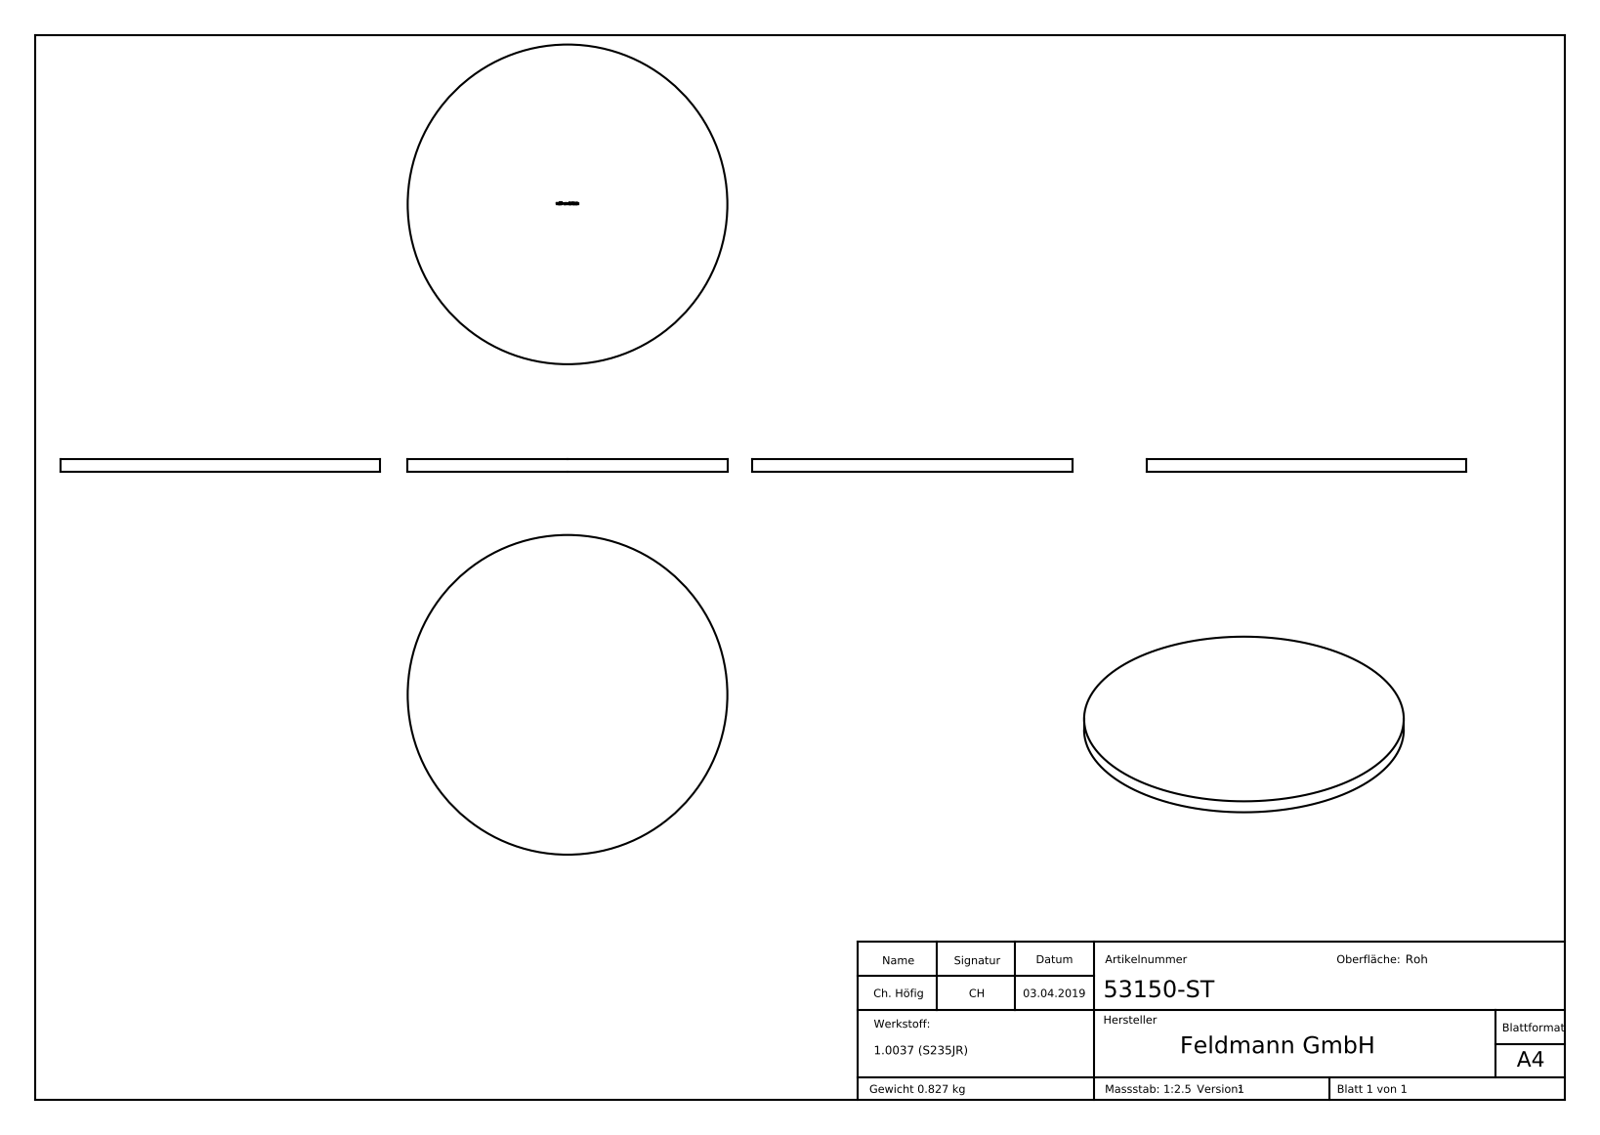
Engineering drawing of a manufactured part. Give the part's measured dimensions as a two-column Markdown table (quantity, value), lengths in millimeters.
| quantity | value |
| --- | --- |
| part name | 53150-ST |
| STEP written by | SolidWorks 2015 (CONFIG_CONTROL_DESIGN) |
| units | millimeters |
| bodies | 1 solid, 215 faces (111 planar, 2 cylindrical, 102 other) |
| overall size | 150 × 150 × 6 |
| volume | 106 029 mm³ |
| surface area | 38 176 mm² |
| round bosses / shafts (diameter × count) | 150 × 1 |
| main face-to-face distances | 6, 5.9, 0.44, 0.79, 0.99, 1.78, 5.83, 1.21, 8.49, 2.66 |
